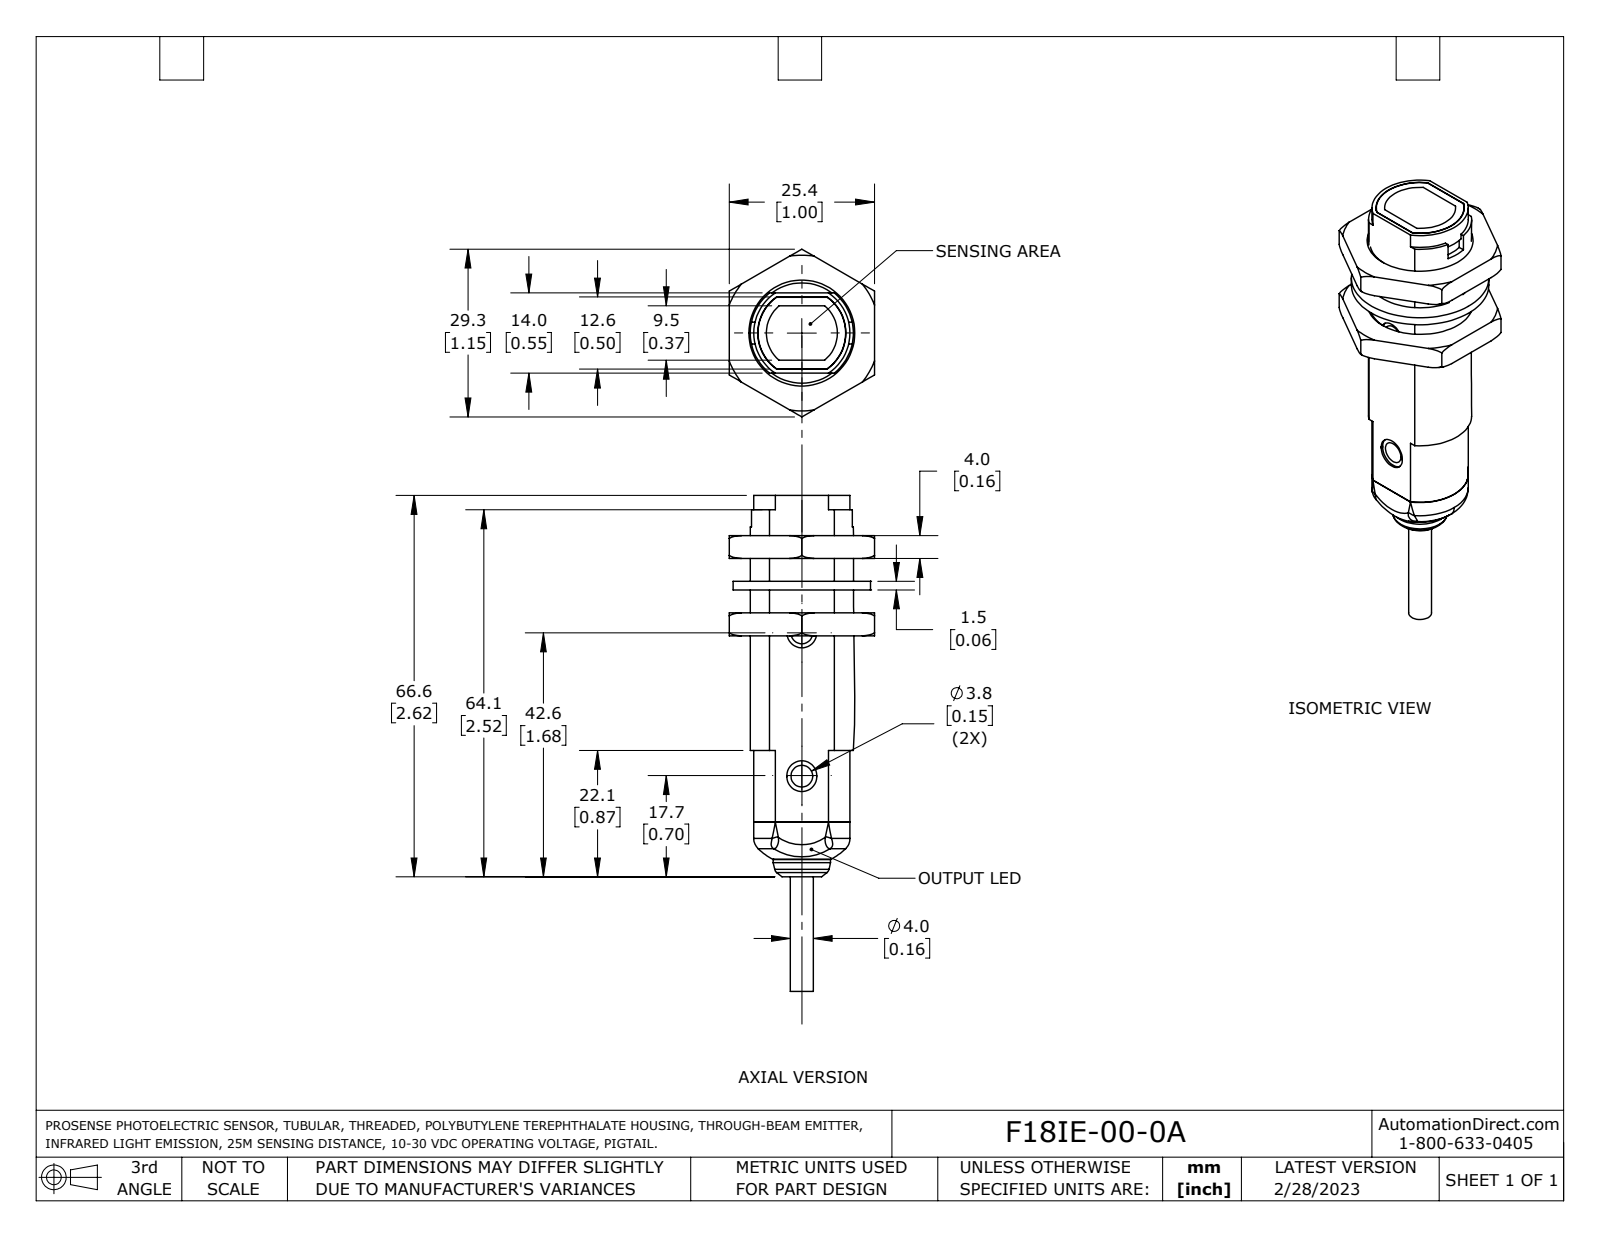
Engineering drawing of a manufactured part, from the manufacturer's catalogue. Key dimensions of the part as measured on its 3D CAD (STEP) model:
Part name (STEP PRODUCT): F18IE-00-0A
STEP written by: SolidWorks 2021 (AUTOMOTIVE_DESIGN)
Units: inches
Bodies: 4 solids, 149 faces (62 planar, 39 cylindrical, 48 other)
Overall size (bounding box): 3.409 × 1.153 × 0.998
Volume: 1.008 in³ · Surface area: 11.59 in²
Round holes (diameter × count): ⌀0.15 ×2, ⌀0.205 ×1, ⌀0.689 ×1, ⌀0.709 ×1
Round bosses / shafts (diameter × count): ⌀0.945 ×1, ⌀0.394 ×1, ⌀0.157 ×1
Partial cylindrical surfaces — rounded edges, fillets, slot ends (radius × count): R0.039 ×4, R0.059 ×4, R0.102 ×2, R1.102 ×2, R0.301 ×1, R0.303 ×1, R0.307 ×1, R0.315 ×1
Main face-to-face distances: 0.157, 0.374, 0.551, 0.531, 0.217, 0.315, 0.998, 0.689, 0.433, 0.059
Hole centre spacings: 0.984
